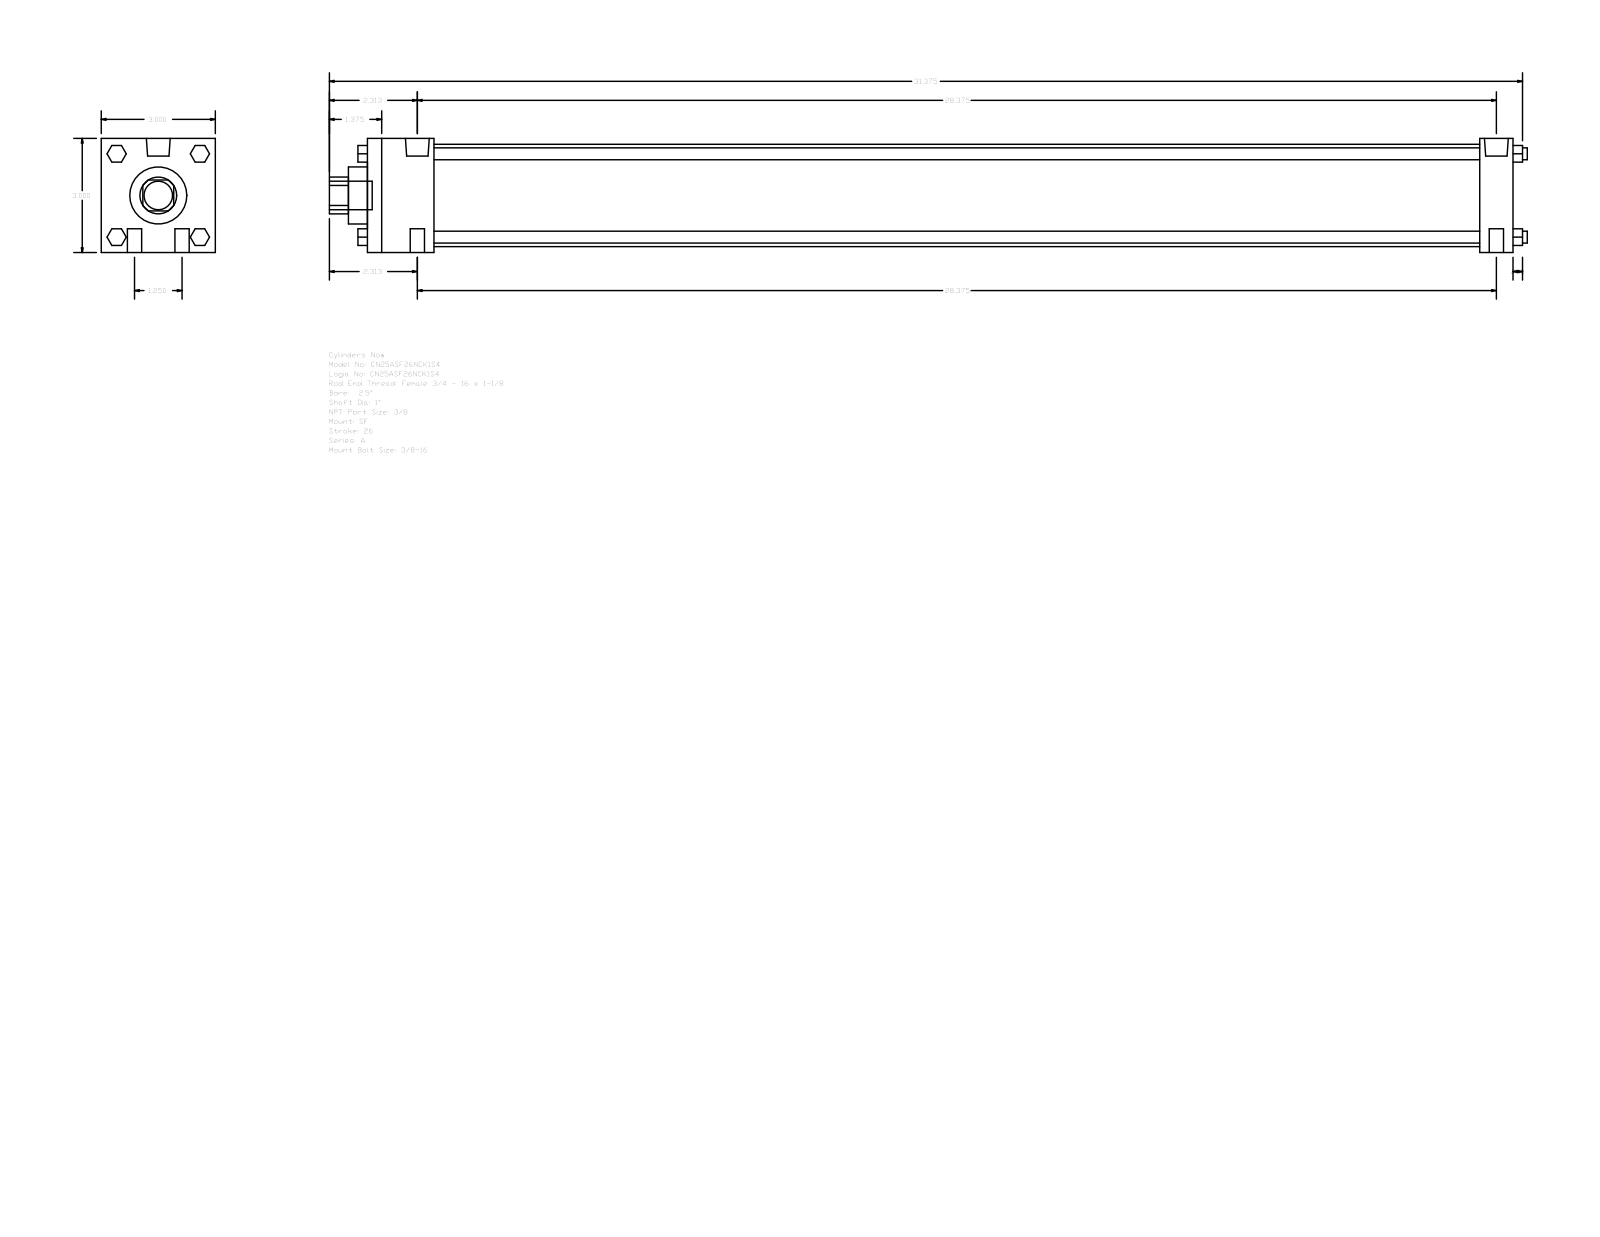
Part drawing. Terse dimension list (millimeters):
name: A_SF__0250_1
written by: GSSL Pune (CONFIG_CONTROL_DESIGN)
unit: mm
bodies: 0 solids, 124 faces (94 planar, 30 cylindrical, 0 other)
size: 800.1 × 76.2 × 76.2
holes: 1× ⌀25.4, 1× ⌀38.1, 1× ⌀68.33
bosses: 4× ⌀9.53, 4× ⌀7.94, 2× ⌀15.93, 2× ⌀5.56, 1× ⌀19.05
rounds: 1× R12.29
face distances: 76.2, 765.18, 742.95, 22.23, 44.45, 698.5, 720.73, 12.7, 11.11, 57.15
